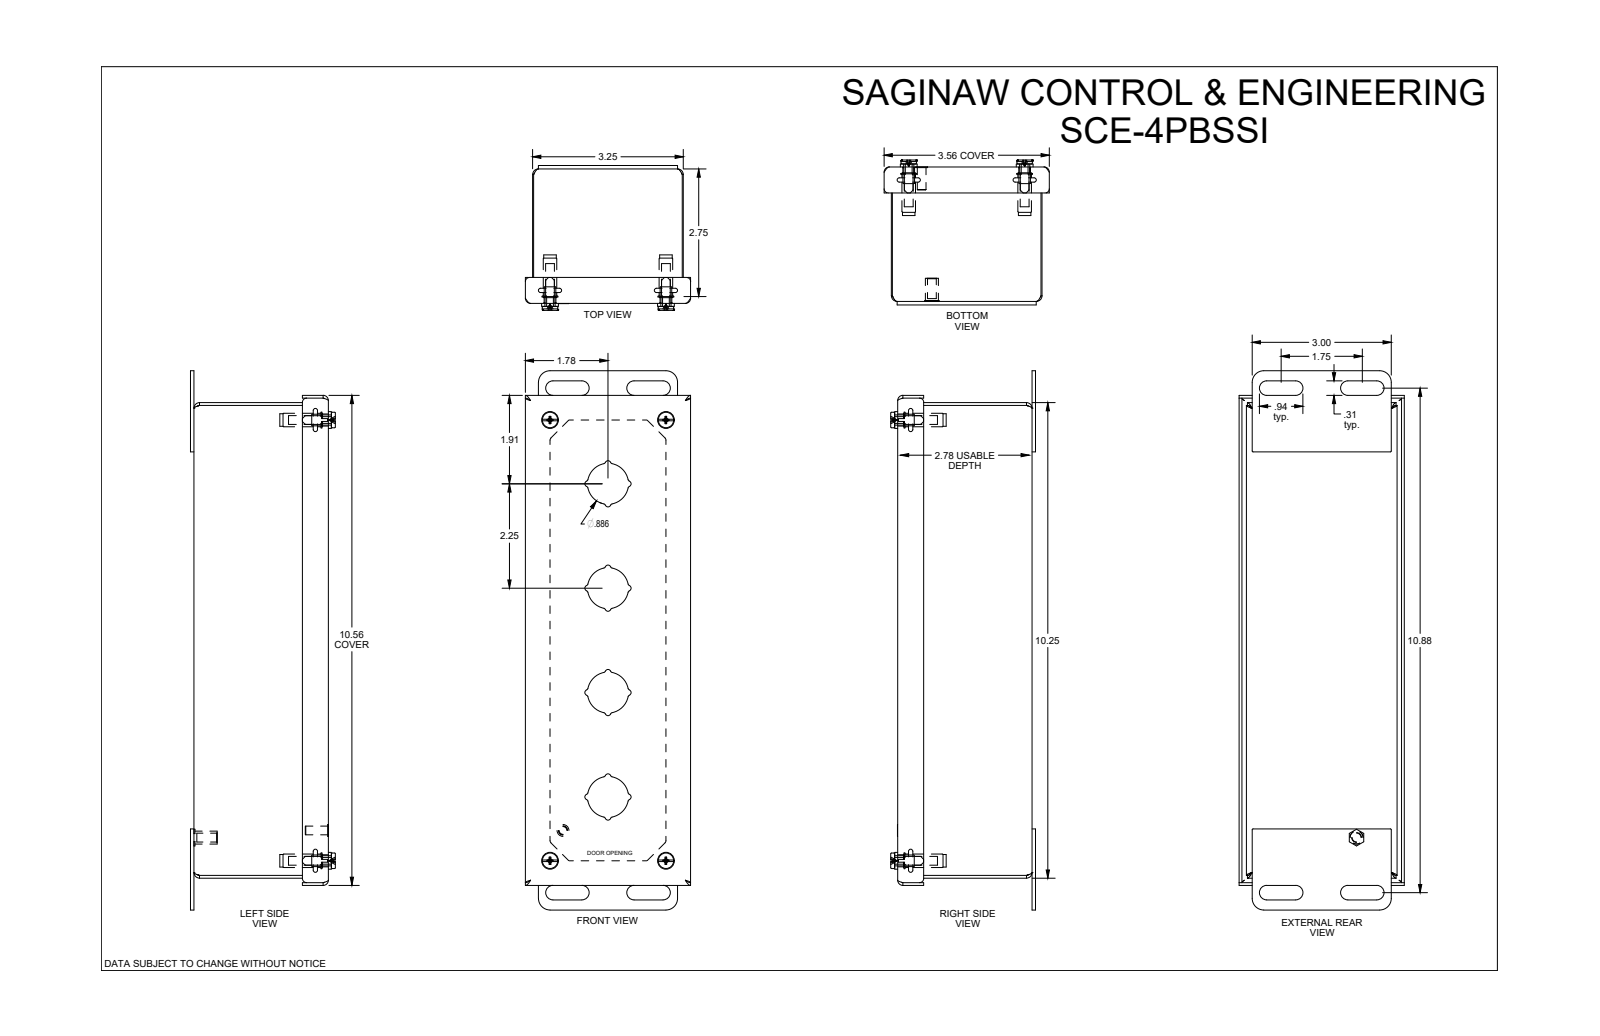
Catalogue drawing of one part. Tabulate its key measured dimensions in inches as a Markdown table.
| quantity | value |
| --- | --- |
| part name | SCE-4PBSSI |
| STEP written by | SolidWorks 2019 (CONFIG_CONTROL_DESIGN) |
| units | inches |
| bodies | 0 solids, 806 faces (382 planar, 262 cylindrical, 162 other) |
| overall size | 11.625 × 3.563 × 3.124 |
| round holes (diameter × count) | 0.19 × 5, 0.22 × 4, 0.25 × 4, 0.266 × 4, 0.193 × 1 |
| round bosses / shafts (diameter × count) | 0.188 × 5, 0.362 × 4, 0.34 × 4, 0.334 × 4, 0.317 × 4, 0.292 × 4, 0.27 × 4, 0.26 × 4 |
| partial cylindrical surfaces (radius × count) | 0.04 × 32, 0.062 × 16, 0.015 × 8, 0.052 × 8, 0.06 × 8, 0.112 × 8, 0.115 × 8, 0.156 × 8 |
| main face-to-face distances | 0.06, 2.838, 3.19, 2.898, 2.778, 3.25, 3.13, 10.19, 2.69, 0.148 |
| hole center spacings | 2.5, 9.5, 9.5, 9.823, 9.824, 0.269, 0.707, 0.711 |
